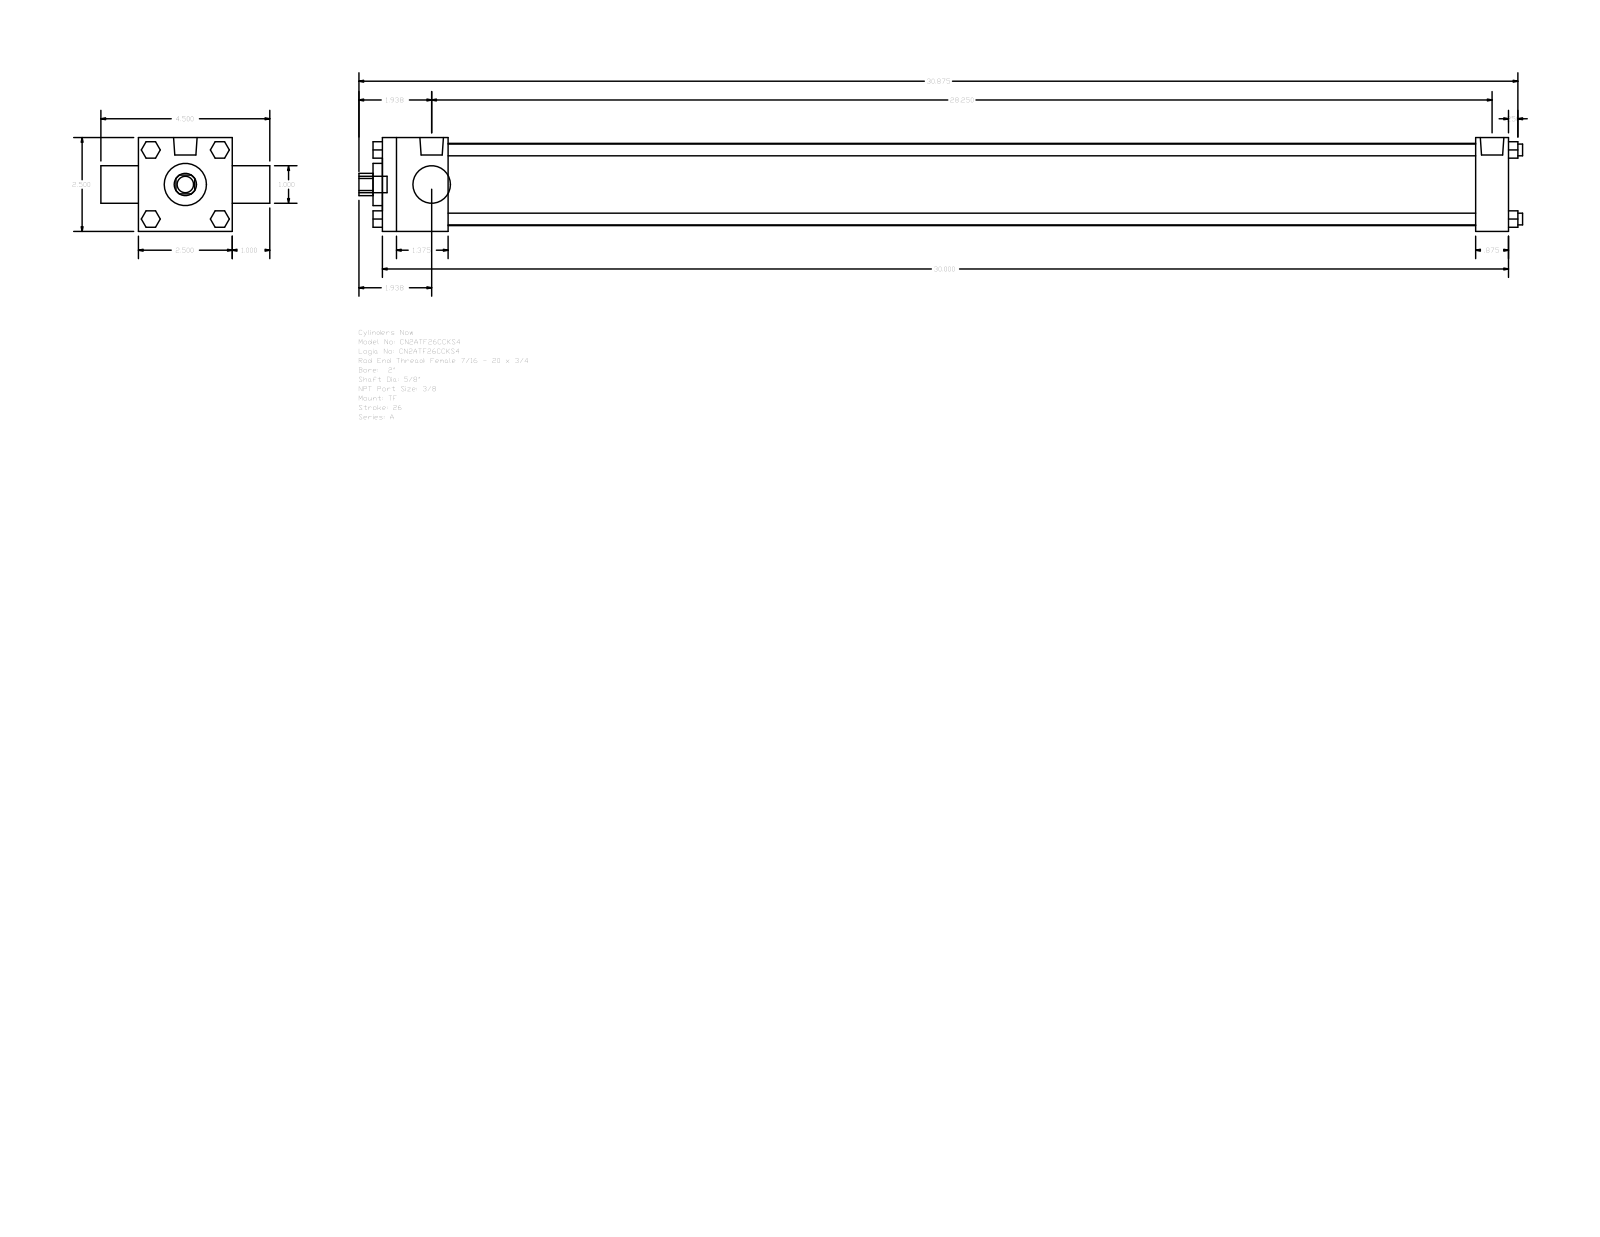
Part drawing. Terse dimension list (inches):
name: A_TF__0200_0.625
written by: GSSL Pune (CONFIG_CONTROL_DESIGN)
unit: in
bodies: 0 solids, 120 faces (92 planar, 28 cylindrical, 0 other)
size: 31 × 4.5 × 2.5
holes: 1× ⌀0.625, 1× ⌀1, 1× ⌀1.125, 1× ⌀2.19
bosses: 4× ⌀0.313, 3× ⌀0.219, 2× ⌀0.627, 1× ⌀0.437
rounds: 1× R0.297
face distances: 2.5, 30, 1.75, 29.125, 27.375, 28.25, 0.875, 1, 3.5, 30.25
